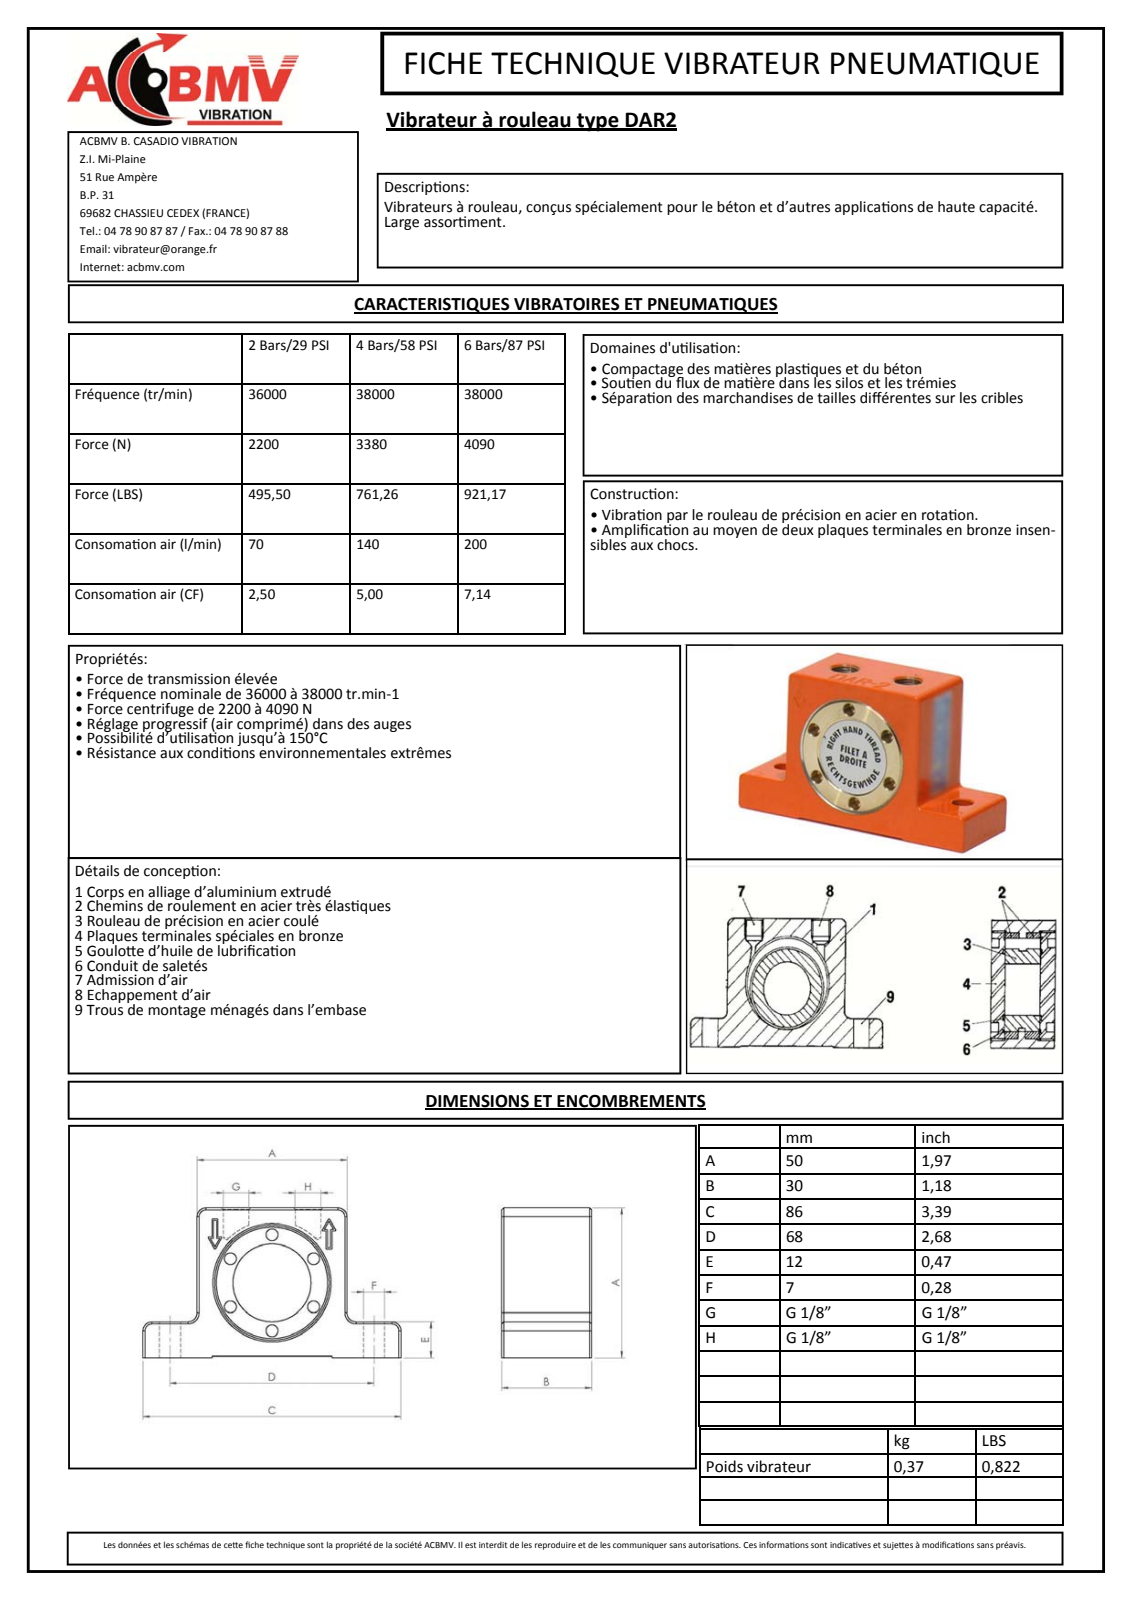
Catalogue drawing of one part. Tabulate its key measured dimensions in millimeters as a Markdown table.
| quantity | value |
| --- | --- |
| part name | 7002-00-M |
| STEP written by | Autodesk Inventor 2011 (CONFIG_CONTROL_DESIGN) |
| units | millimeters |
| bodies | 1 solid, 329 faces (199 planar, 90 cylindrical, 40 other) |
| overall size | 86 × 50 × 30 |
| volume | 83 899 mm³ |
| surface area | 15 440 mm² |
| round holes (diameter × count) | 4 × 6, 7 × 2, 8.57 × 2, 2.09 × 1, 26 × 1 |
| round bosses / shafts (diameter × count) | 1.88 × 1 |
| partial cylindrical surfaces (radius × count) | 0.25 × 27, 3 × 6, 0.54 × 4, 0.36 × 3, 0.63 × 3, 0.72 × 3, 1.25 × 3, 1.44 × 3 |
| main face-to-face distances | 0.5, 30, 50, 29.5, 49.5, 38, 12, 11.5, 29, 18 |
| hole center spacings | 16, 27.71, 22, 27.72, 32.01, 46, 10.98, 21.84 |
